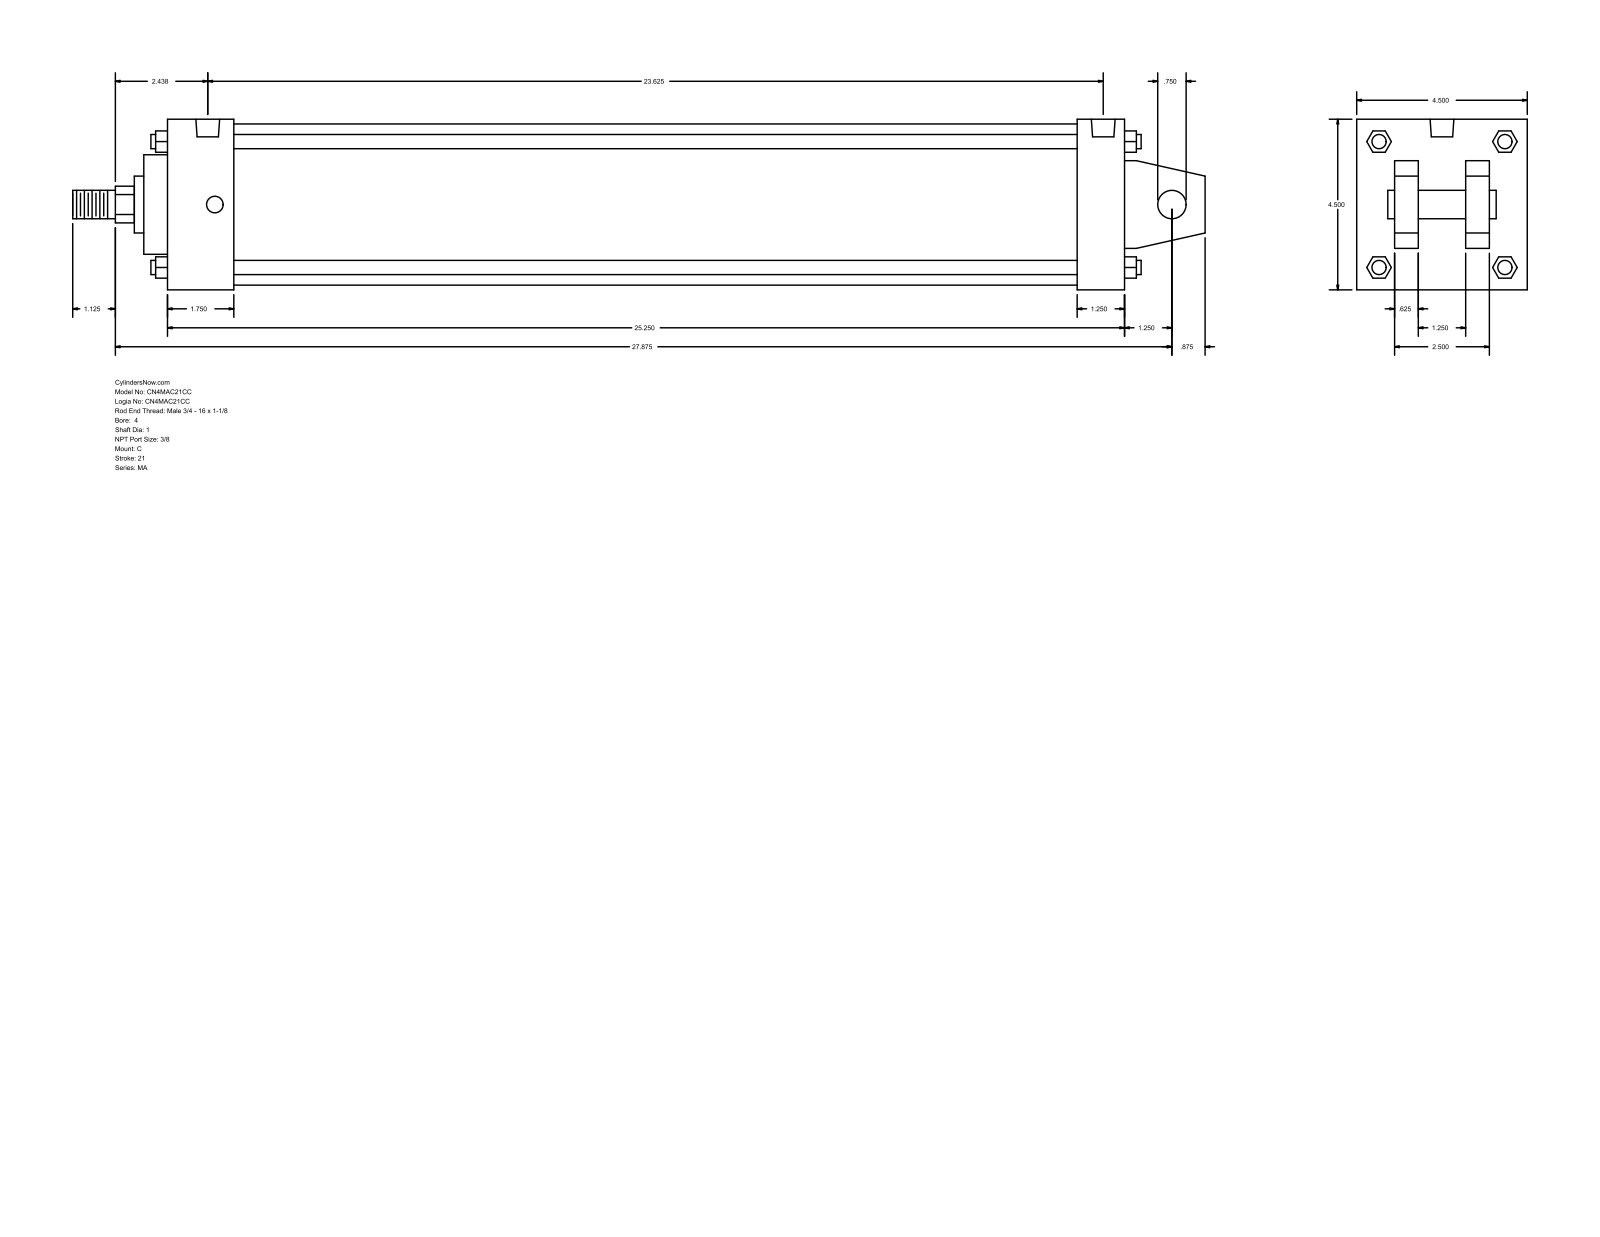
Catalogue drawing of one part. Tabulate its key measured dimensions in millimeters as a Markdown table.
| quantity | value |
| --- | --- |
| part name | MA_C__0400_1 |
| STEP written by | GSSL Pune (CONFIG_CONTROL_DESIGN) |
| units | millimeters |
| bodies | 0 solids, 141 faces (109 planar, 32 cylindrical, 0 other) |
| overall size | 758.83 × 114.3 × 114.3 |
| round holes (diameter × count) | 11.11 × 4, 15.93 × 2 |
| round bosses / shafts (diameter × count) | 9.53 × 4, 19.05 × 2, 107.95 × 1, 66.67 × 1, 38.1 × 1, 25.4 × 1 |
| partial cylindrical surfaces (radius × count) | 12.29 × 1 |
| main face-to-face distances | 114.3, 641.35, 15.87, 73.03, 41.27, 25.4, 88.9, 47.63, 609.6, 31.75 |
| hole center spacings | 4.76, 590.56, 595.32, 600.08 |
